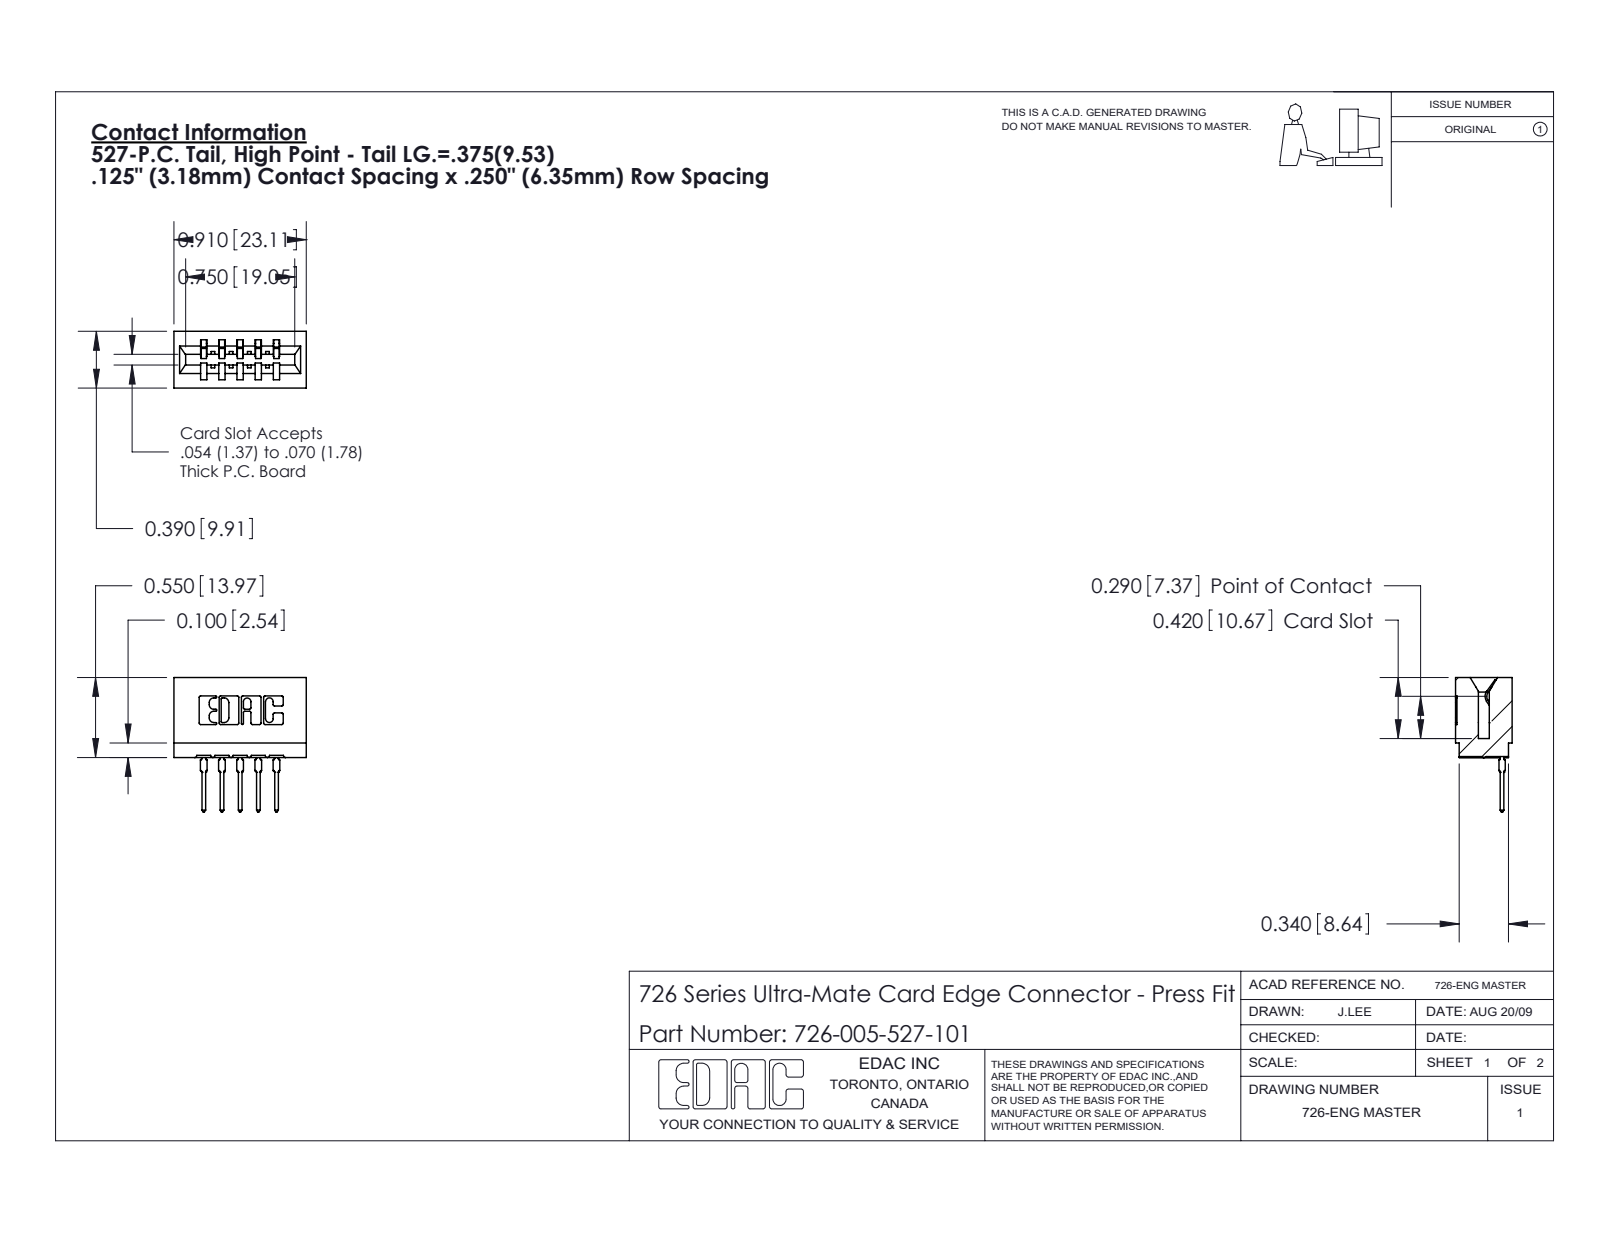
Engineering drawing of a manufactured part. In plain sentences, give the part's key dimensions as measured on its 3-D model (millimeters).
The part is named "726-005-527-101; 746-292-001_527; 726 Part_.515 Slot Depth - 01". Its 3-D file was written by "SolidWorks 2020 (CONFIG_CONTROL_DESIGN)". It is 6 solids with 637 faces: 370 planar, 137 cylindrical and 130 other. Overall it measures 23.5 by 23.1 by 9.9 millimeters. Its volume is 2 280 cubic millimeters and its surface area 2 965 square millimeters. Partial cylindrical surfaces (rounded edges, fillets, slot ends): 22 of radius 0.3, 10 of radius 0.5, 6 of radius 0.2, 6 of radius 0.4, 6 of radius 0.8, 4 of radius 0.1, 4 of radius 0.3, 3 of radius 0.7. The main face-to-face distances are 6.4, 1.1, 1.4, 8.5, 3.2, 3.2, 9.9, 2.1, 7.4, 5.3.
